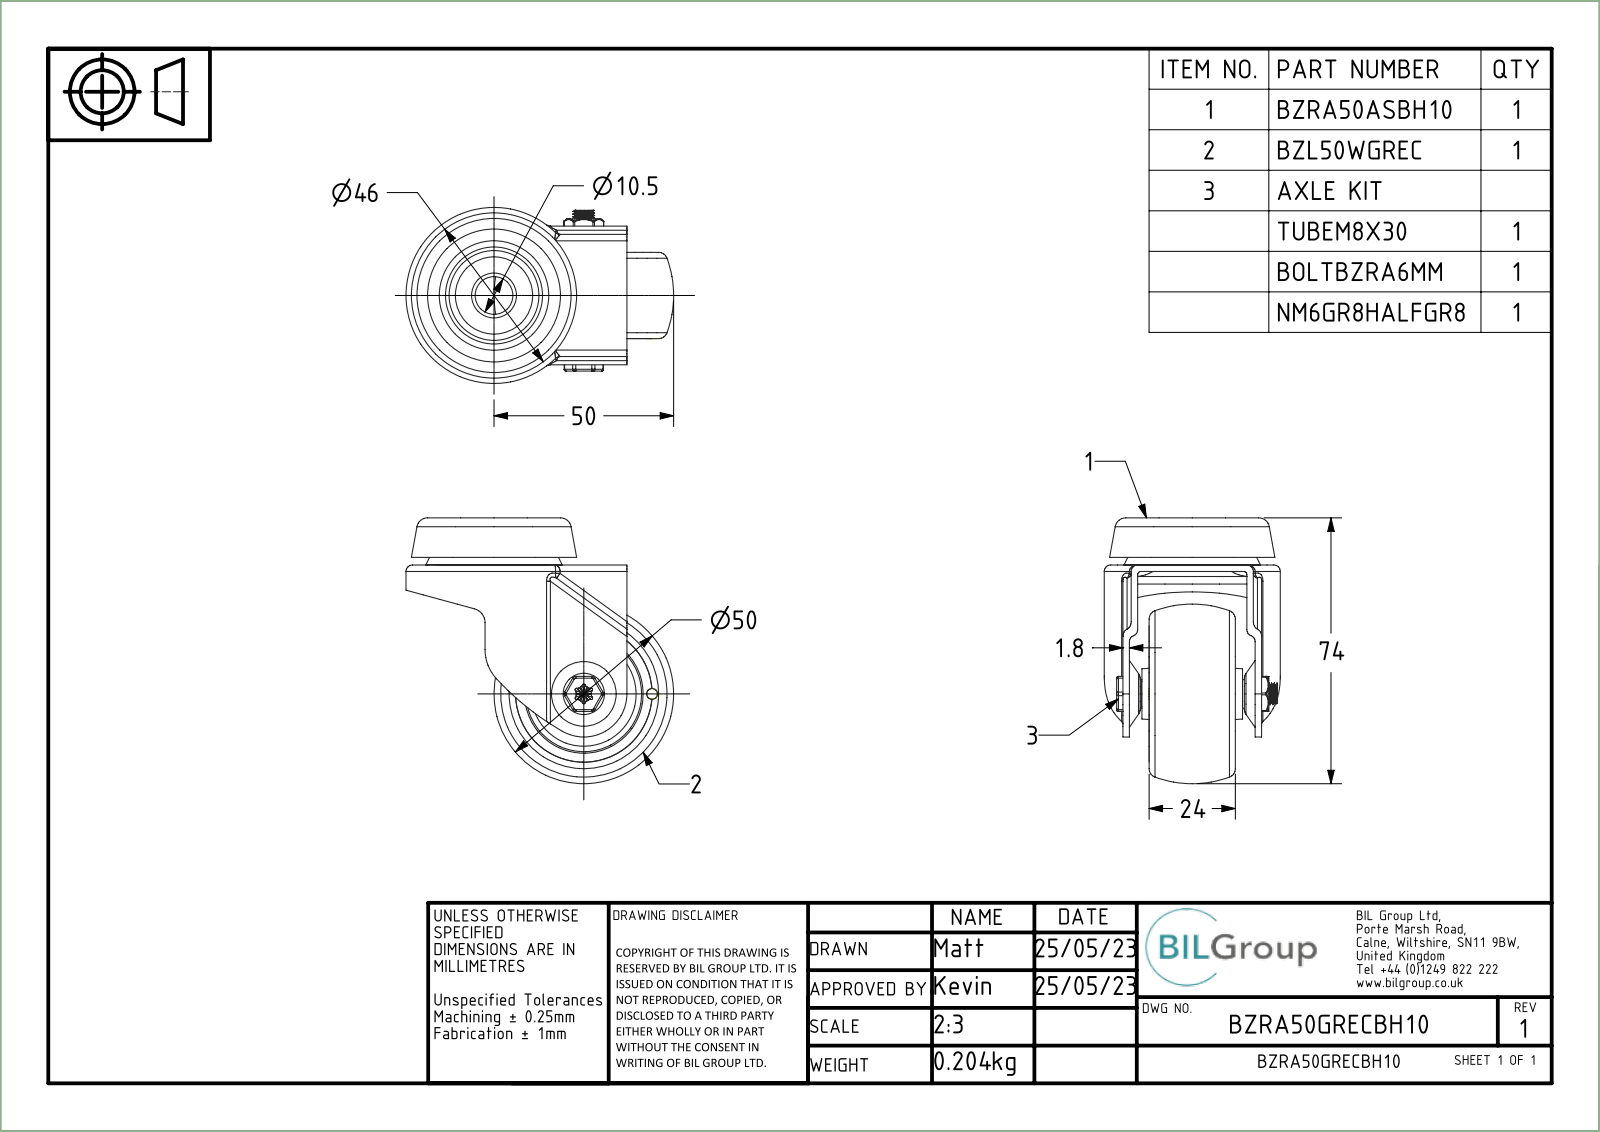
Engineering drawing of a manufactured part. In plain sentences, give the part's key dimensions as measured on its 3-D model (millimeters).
The part is named "BZRA50ASBH10; ZINC PLATED PRESSED STEEL FORKS; ZINC PLATED PRESSED STEEL HEAD; BZRA50GRECBH10 (+8 more)". Its 3-D file was written by "Spatial InterOp 3D (CONFIG_CONTROL_DESIGN)". It is 8 solids with 410 faces: 64 planar, 174 cylindrical and 172 other. Overall it measures 74 by 72.66 by 49 millimeters. Its volume is 50 525 cubic millimeters and its surface area 41 090 square millimeters. Round holes: 1 of diameter 3, 1 of diameter 6, 1 of diameter 6.2, 1 of diameter 6.3, 1 of diameter 8.2, 1 of diameter 10.5, 1 of diameter 10.56, 1 of diameter 38. Round bosses or shafts: 1 of diameter 39, 1 of diameter 38, 1 of diameter 18, 1 of diameter 14.76, 1 of diameter 8, 1 of diameter 7.95, 1 of diameter 5. Partial cylindrical surfaces (rounded edges, fillets, slot ends): 18 of radius 1, 14 of radius 1.8, 12 of radius 0.5, 6 of radius 0.4, 6 of radius 0.9, 2 of radius 12, 1 of radius 2.12, 1 of radius 4. The main face-to-face distances are 1.8, 10, 34.5, 2.3, 14, 4.1, 1, 13.12, 14.92, 36.8. The hole center spacings are 19.
